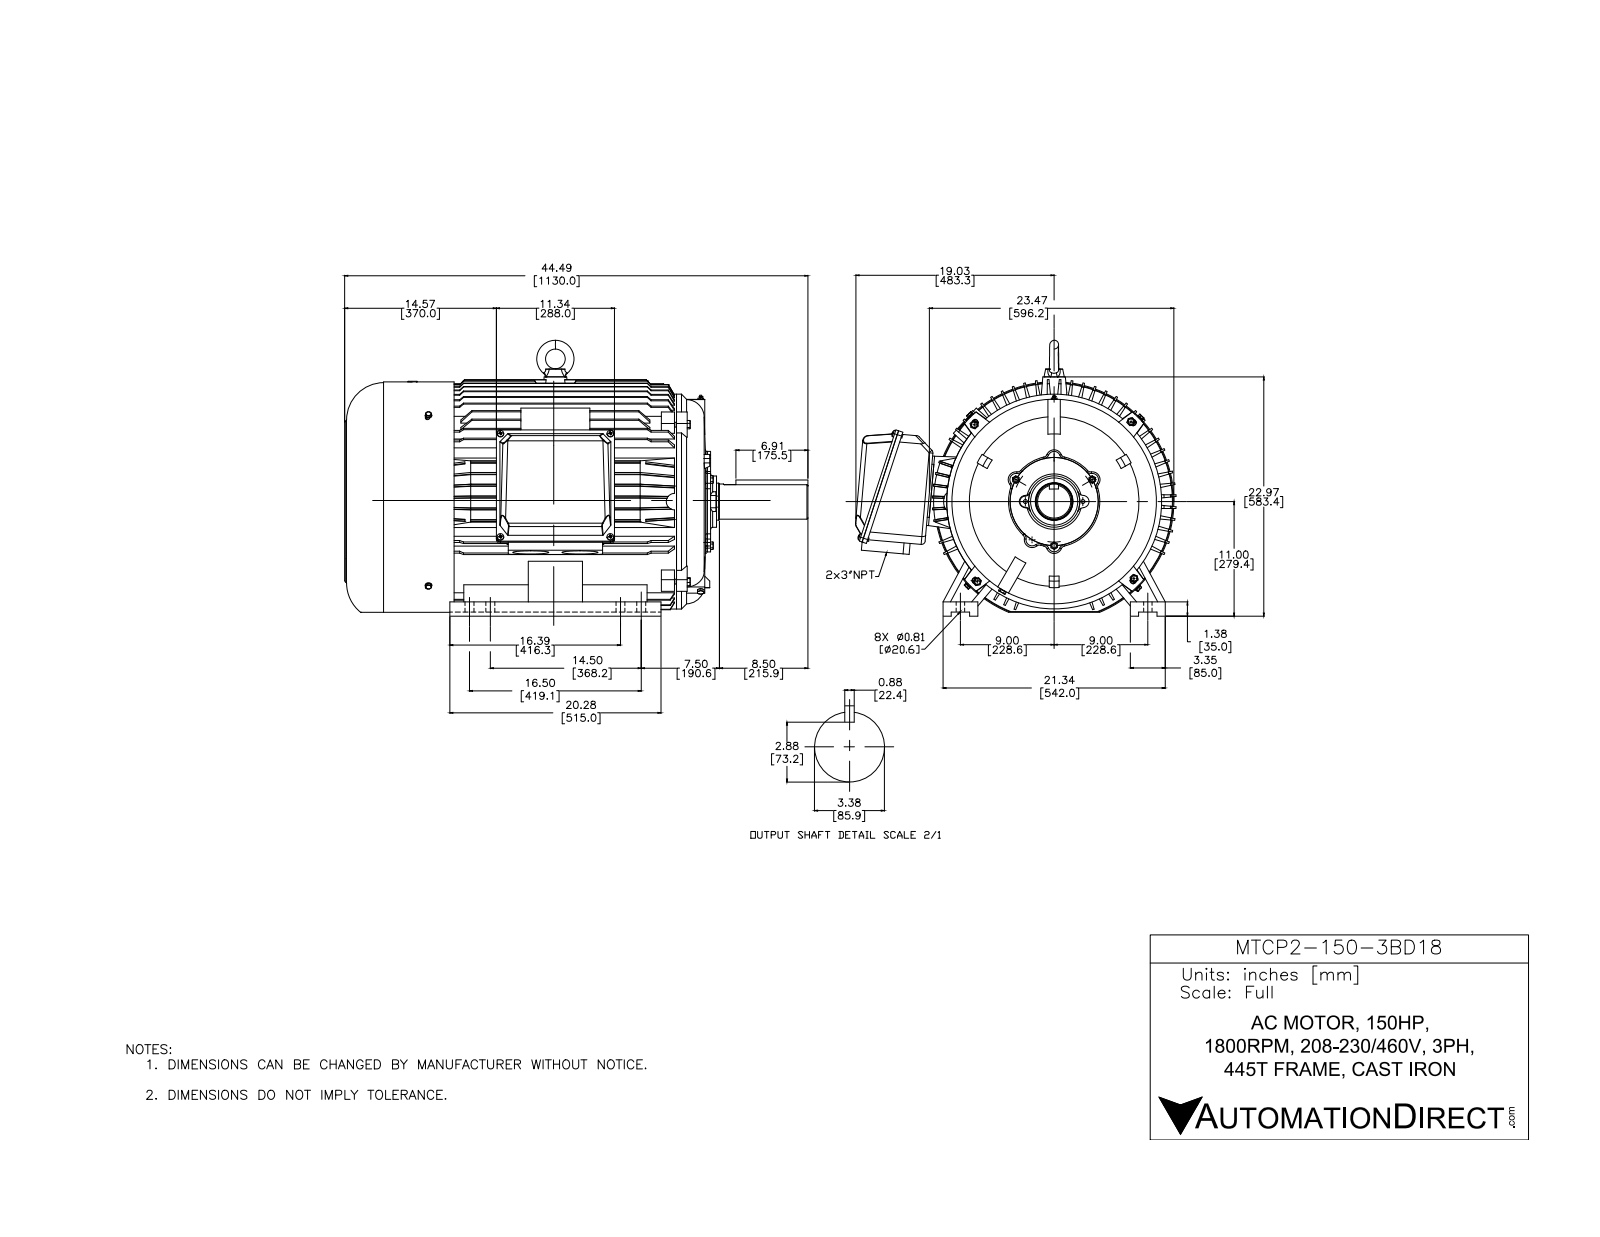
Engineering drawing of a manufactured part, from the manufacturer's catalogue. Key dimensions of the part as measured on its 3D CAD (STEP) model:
Part name (STEP PRODUCT): PEWWE-445T-468P
STEP written by: SolidWorks 2017 (AUTOMOTIVE_DESIGN)
Units: inches
Bodies: 44 solids, 4120 faces (3168 planar, 497 cylindrical, 455 other)
Overall size (bounding box): 44.488 × 30.775 × 26.488
Volume: 2 324 in³ · Surface area: 10 195 in²
Round holes (diameter × count): ⌀0.315 ×12, ⌀0.827 ×8, ⌀0.472 ×5, ⌀0.331 ×4, ⌀0.394 ×4, ⌀0.539 ×4, ⌀0.542 ×4, ⌀0.591 ×4, ⌀0.441 ×3, ⌀0.276 ×2, ⌀3.465 ×2, ⌀0.079 ×1
Round bosses / shafts (diameter × count): ⌀0.63 ×8, ⌀0.315 ×8, ⌀0.472 ×4, ⌀0.394 ×4, ⌀0.428 ×3, ⌀0.355 ×3, ⌀22.989 ×1, ⌀20.63 ×1
Partial cylindrical surfaces — rounded edges, fillets, slot ends (radius × count): R0.591 ×23, R0.012 ×16, R0.354 ×11, R0.079 ×10, R0.197 ×8, R0.394 ×8, R0.787 ×6, R0.236 ×2
Main face-to-face distances: 0.059, 0.236, 0.079, 7.006, 0.709, 6.769, 1.008, 0.929, 0.984, 0.024
Hole centre spacings: 4.232, 10.551, 10.728, 10.655, 0.219, 2, 2.756, 5.05
